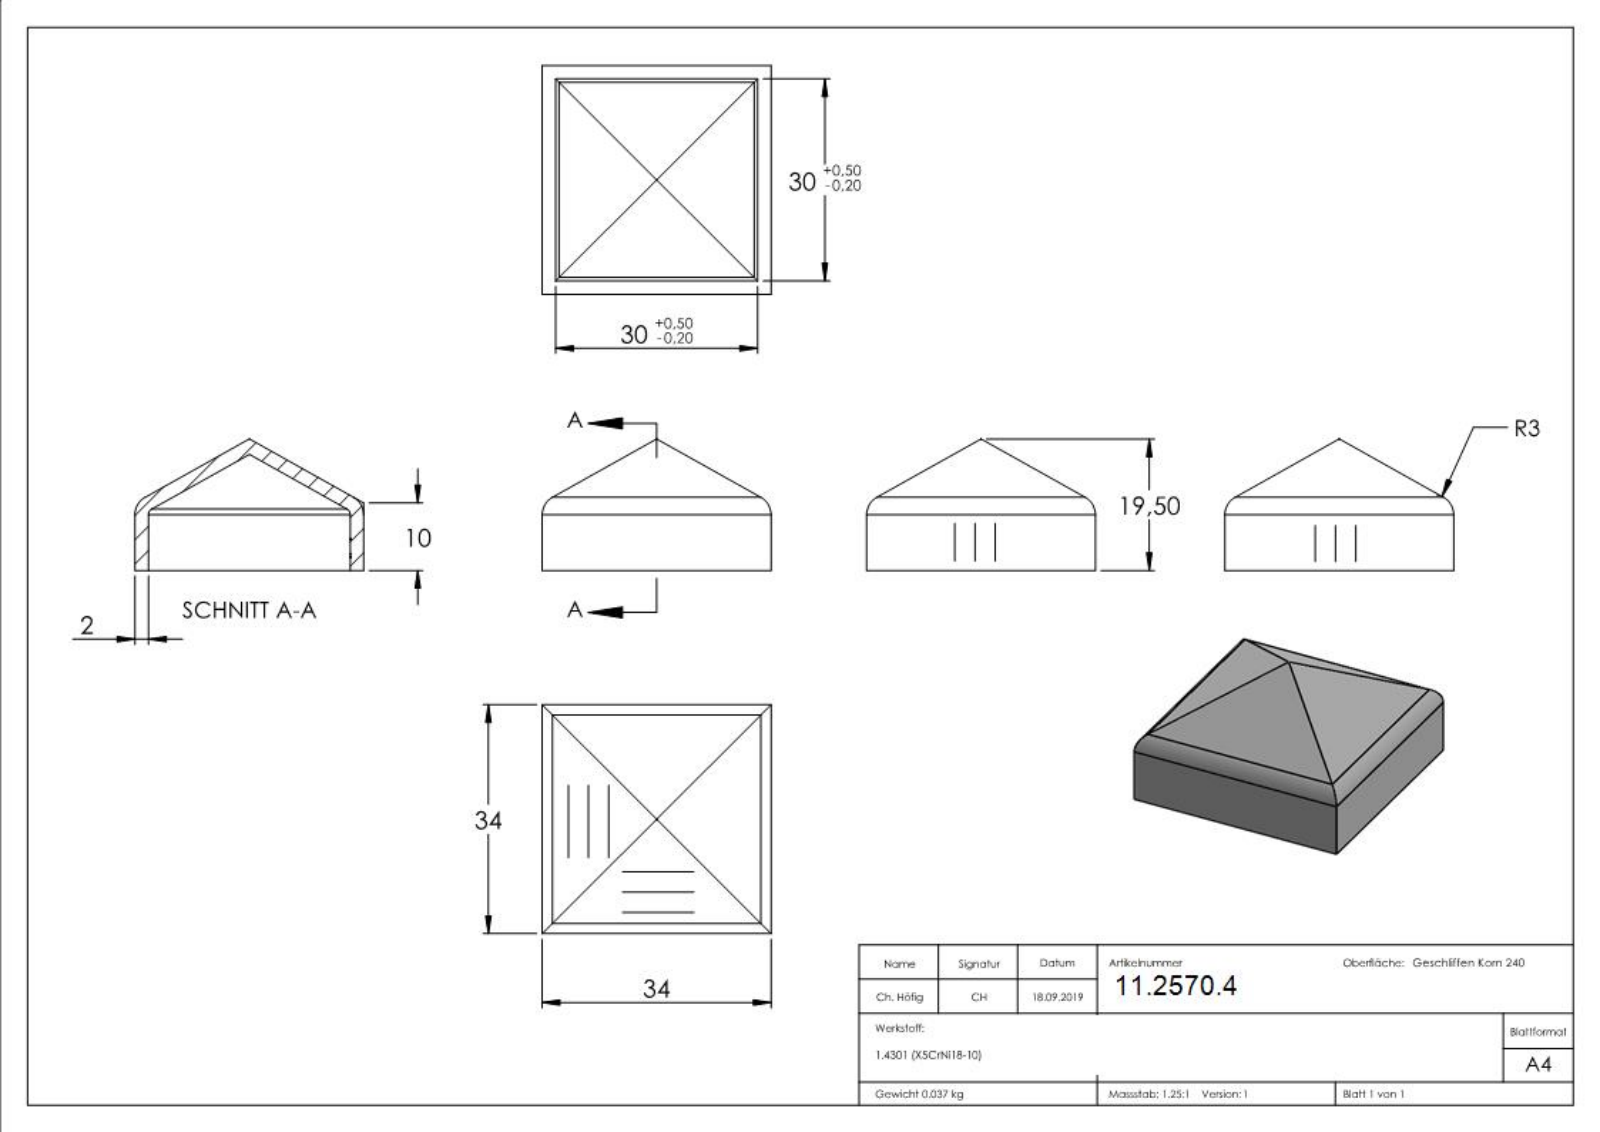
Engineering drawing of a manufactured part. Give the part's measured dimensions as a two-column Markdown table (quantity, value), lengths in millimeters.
| quantity | value |
| --- | --- |
| part name | 165-30V2AG |
| STEP written by | SolidWorks 2015 (CONFIG_CONTROL_DESIGN) |
| units | millimeters |
| bodies | 1 solid, 260 faces (145 planar, 12 cylindrical, 103 other) |
| overall size | 34 × 34 × 19.5 |
| volume | 4 702 mm³ |
| surface area | 4 975 mm² |
| partial cylindrical surfaces (radius × count) | 1 × 4, 3 × 4, 0.1 × 2 |
| main face-to-face distances | 2, 32, 34, 30, 1.9, 30.1, 32.1, 0.45, 1.66, 1.78 |
